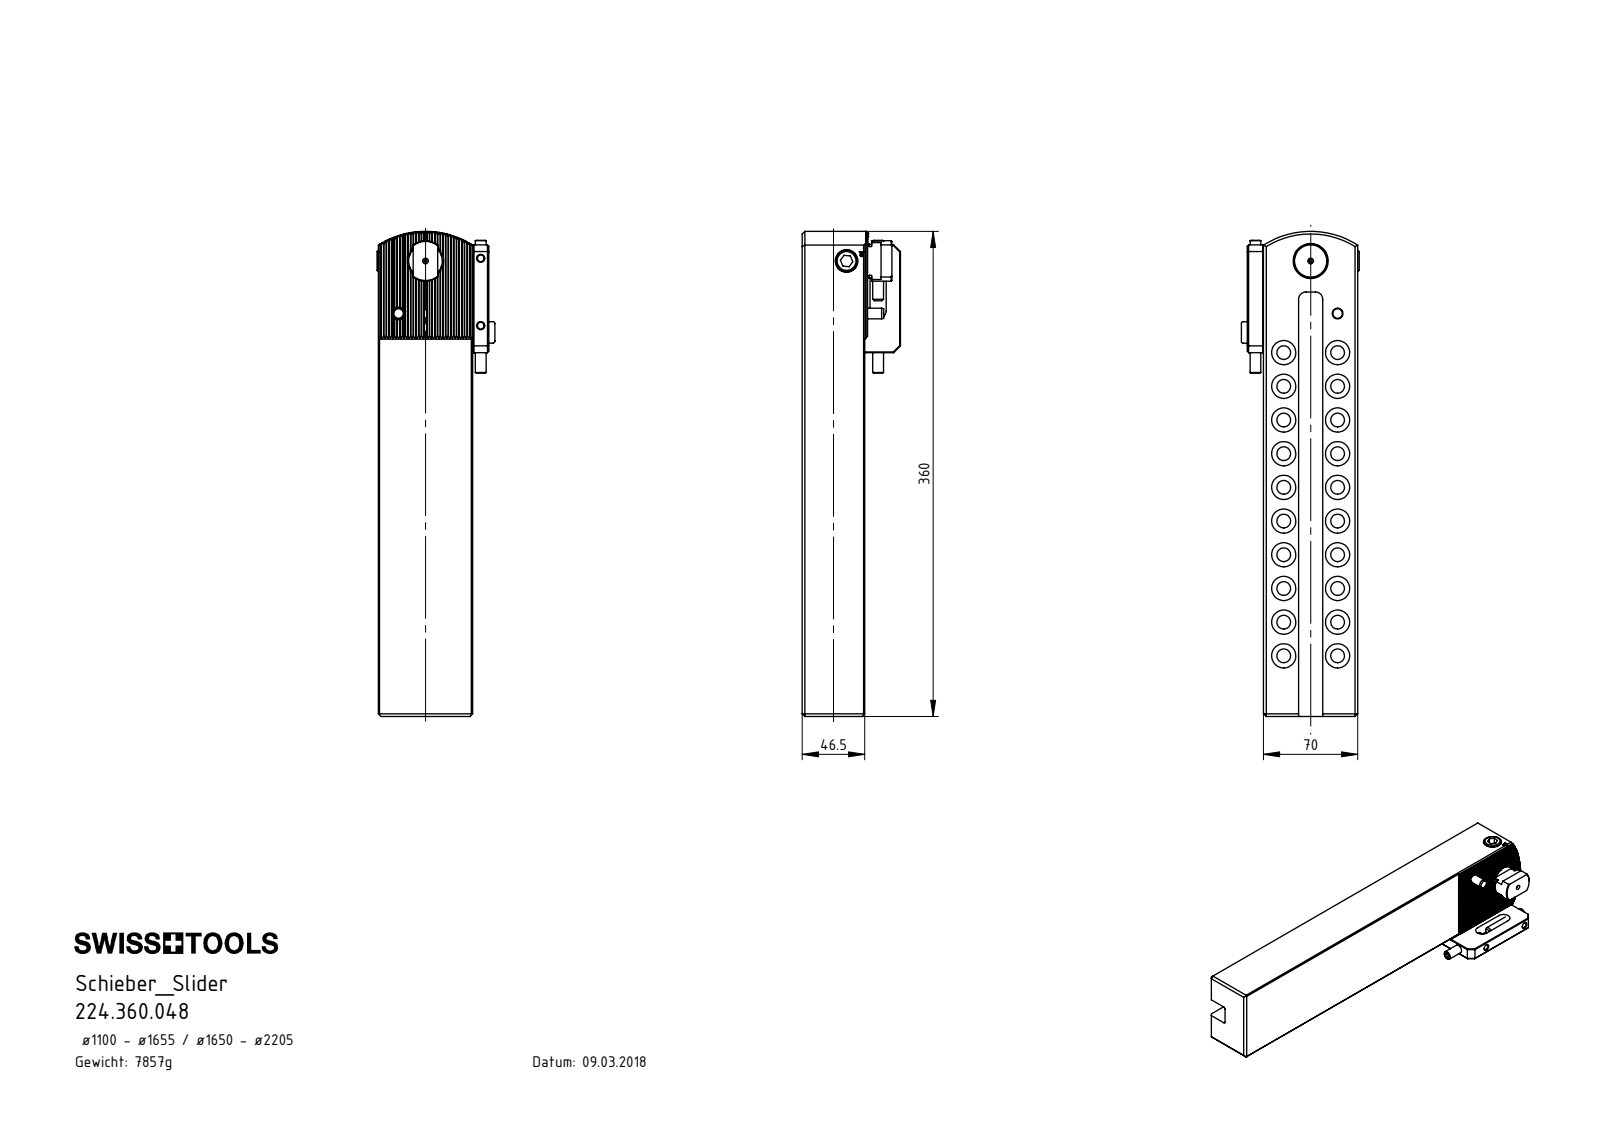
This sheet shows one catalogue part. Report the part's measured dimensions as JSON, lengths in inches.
{"part_name": "VK1-ER2.001.044_A; VK1-ER1.001.030_A; VK1-ER2.101.010_A; VK1-ER2.201.010_A_vorgespannt (+6 more)", "step_written_by": "SolidWorks 2017 (CONFIG_CONTROL_DESIGN)", "units": "inches", "bodies": {"solids": 10, "faces": 724, "planar": 319, "cylindrical": 247, "other": 158}, "overall_size": [14.173, 3.445, 2.874], "volume_in3": 61.08, "surface_area_in2": 252.4, "round_holes": [[0.709, 21], [0.402, 20], [0.197, 2], [0.236, 2], [0.268, 2], [0.079, 1], [0.315, 1], [0.335, 1], [0.413, 1], [0.433, 1], [0.551, 1], [0.984, 1]], "round_bosses_or_shafts": [[0.63, 2], [0.394, 1], [0.315, 1]], "partial_cylinders_radius": [[0.006, 33], [0.079, 4], [0.059, 3], [0.217, 2], [0.236, 2], [0.484, 1], [0.591, 1], [2.559, 1]], "face_to_face_distances": [2.756, 1.831, 1.732, 1.024, 1.043, 0.709, 0.787, 0.256, 1.575, 0.531], "hole_center_spacings": [0.984, 1.857, 1.969, 2.521, 2.953, 3.346, 3.937, 4.24]}
